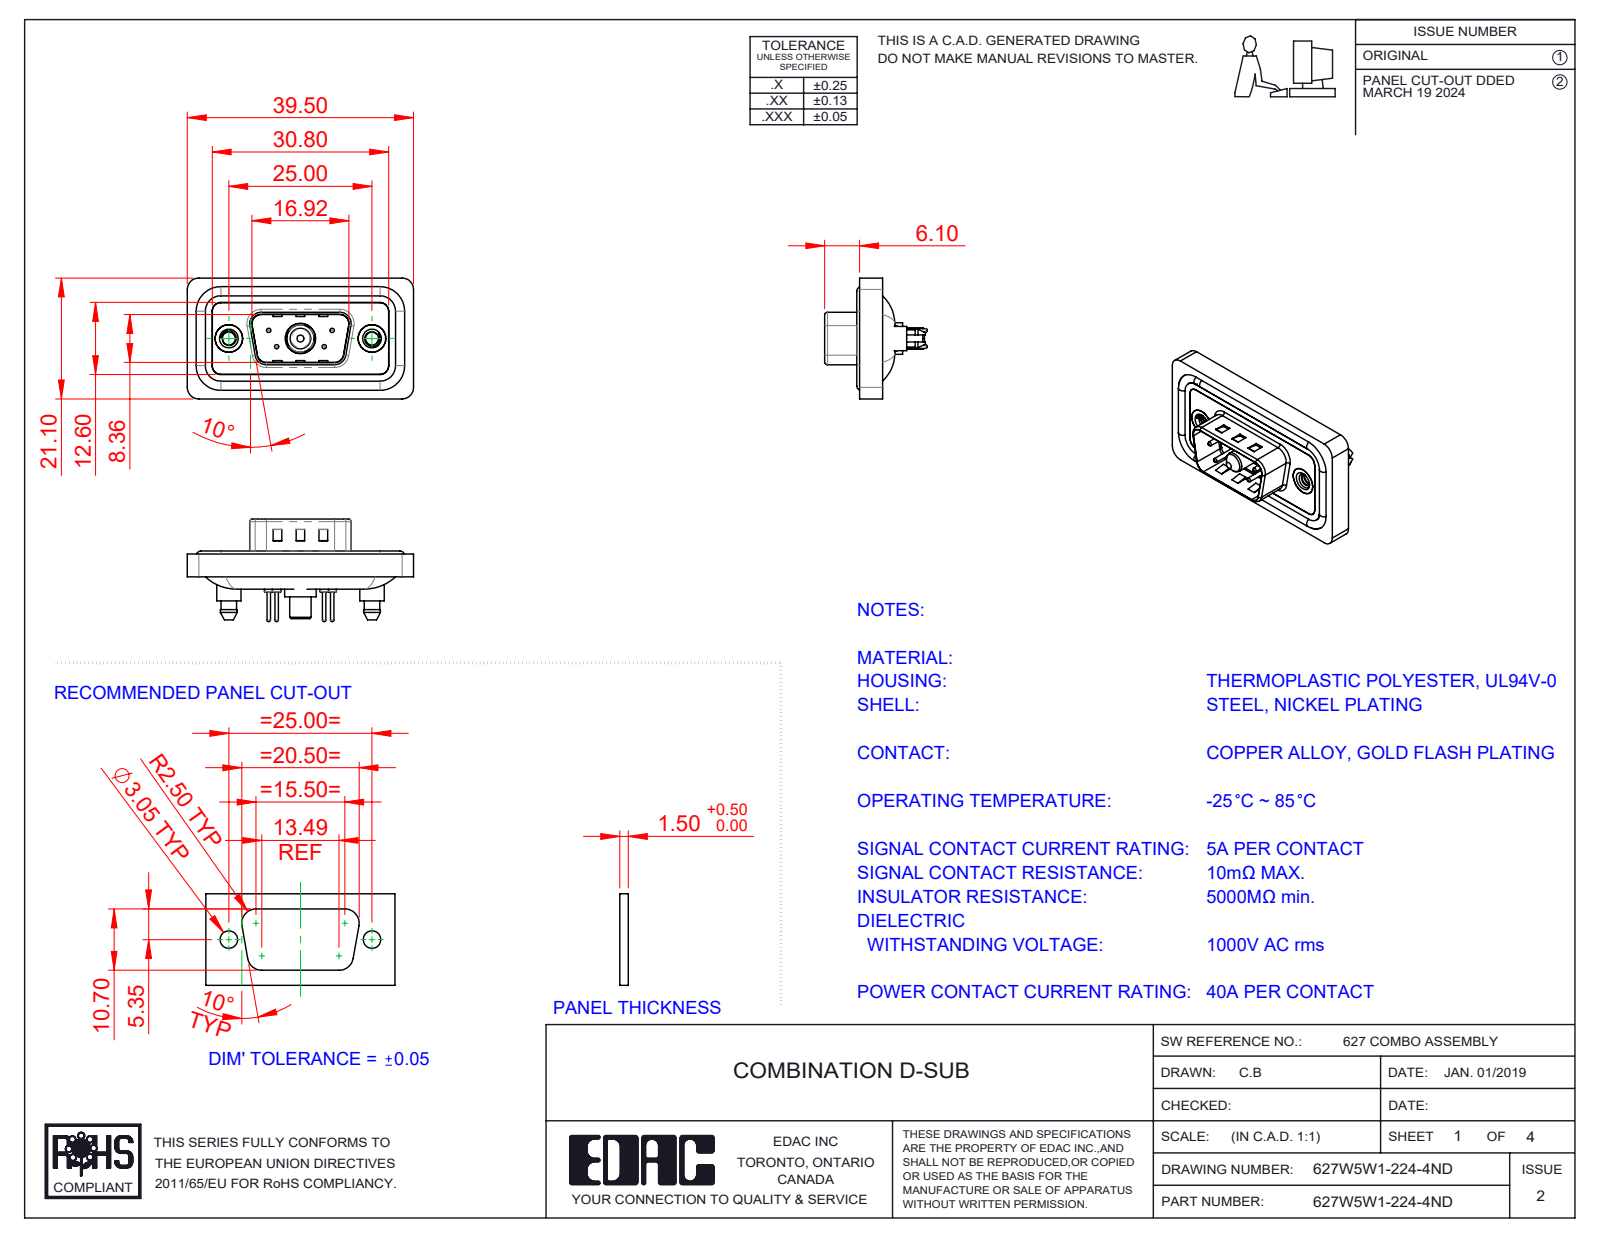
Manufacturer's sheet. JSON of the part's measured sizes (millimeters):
{"part_name": "Power Pin_40A S; 627Combo Threaded Boardlock_5; 627Combo Contact Row 1_24; 627W5W1-224-4ND (+6 more)", "step_written_by": "SolidWorks 2023 (CONFIG_CONTROL_DESIGN)", "units": "millimeters", "bodies": {"solids": 13, "faces": 656, "planar": 199, "cylindrical": 295, "other": 162}, "overall_size": [39.5, 21.1, 17.9], "volume_mm3": 4541, "surface_area_mm2": 7288, "round_holes": [[0.75, 4], [1.6, 4], [2, 4], [2.26, 2], [4, 2], [4.8, 2], [5, 2], [4.85, 1], [5.3, 1]], "round_bosses_or_shafts": [[1.6, 4], [1.5, 4], [0.6, 4], [5.4, 2], [4.9, 2], [4.25, 2], [5.5, 1], [5.2, 1]], "partial_cylinders_radius": [[1.5, 24], [2, 18], [1.6, 10], [0.5, 8], [0.25, 4], [0.6, 4], [0.65, 4], [0.9, 4]], "face_to_face_distances": [0.4, 1.1, 2.9, 1.6, 3.1, 1.5, 0.5, 2.5, 4, 0.8], "hole_center_spacings": [3.16, 5.72, 7.1, 12.5, 18.1, 4.39, 4.4, 8.31]}
